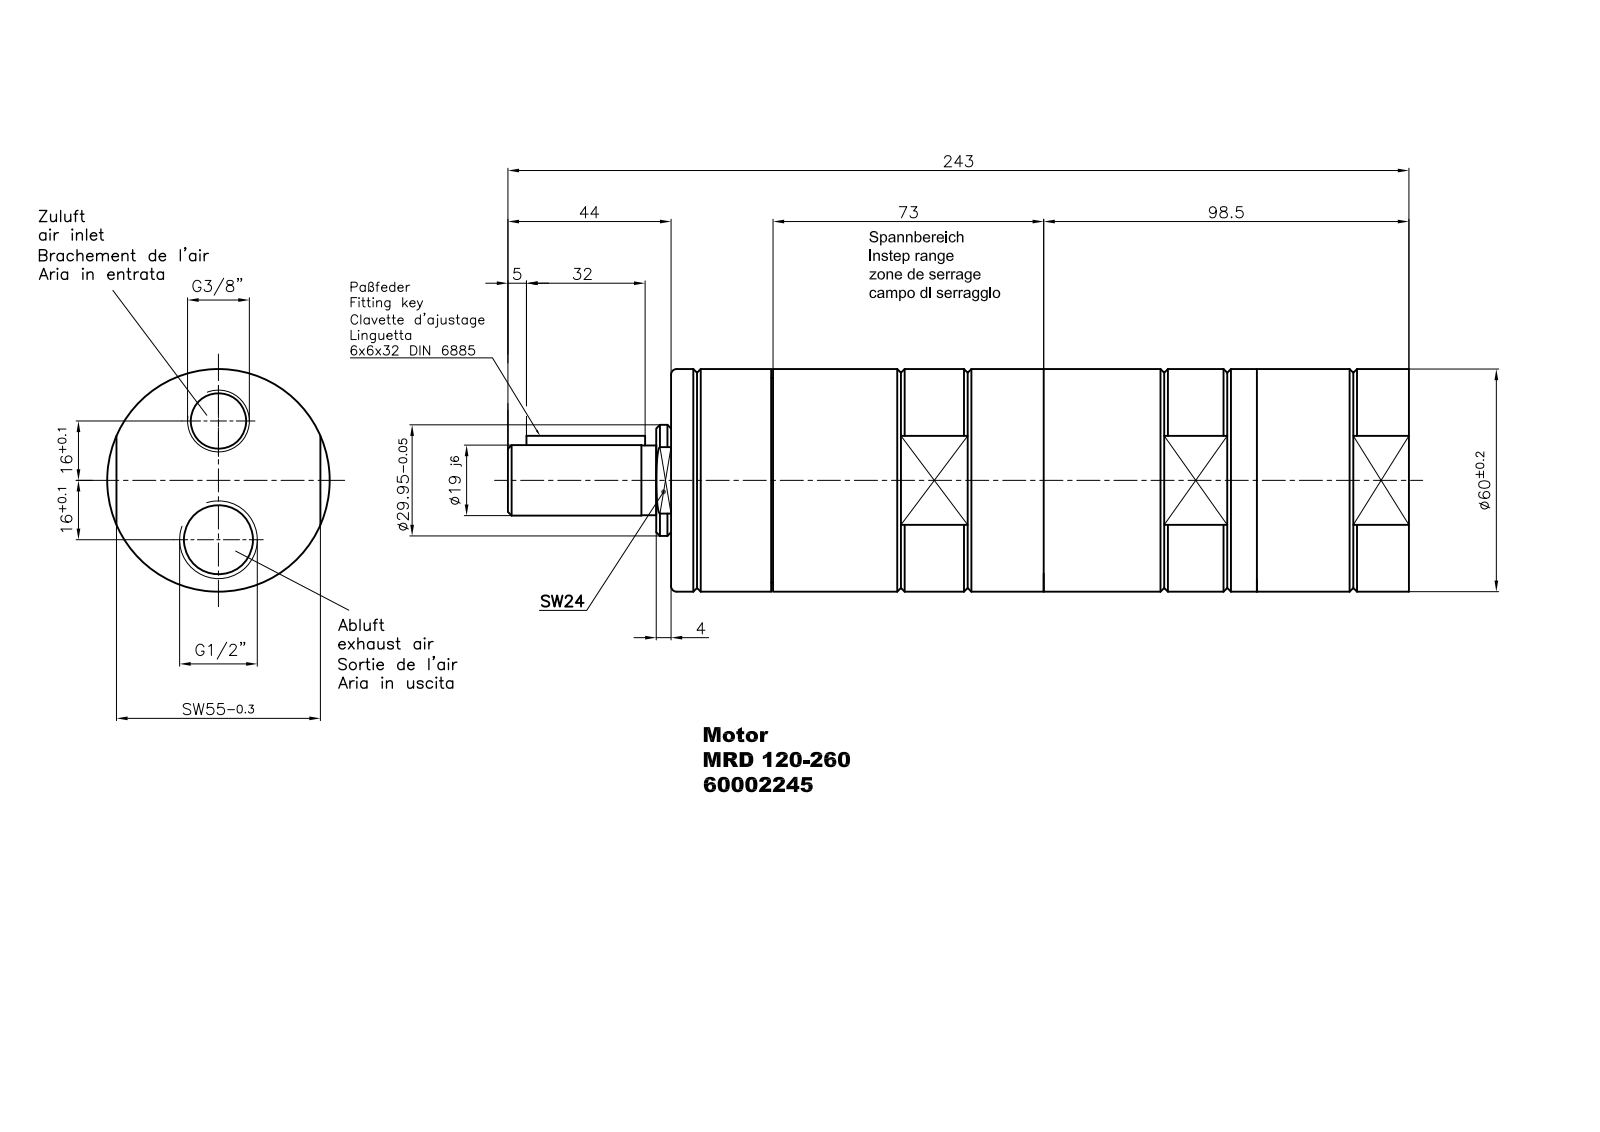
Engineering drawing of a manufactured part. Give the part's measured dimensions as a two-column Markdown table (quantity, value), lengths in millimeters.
| quantity | value |
| --- | --- |
| part name | MRD 120-260_60002245 |
| STEP written by | Autodesk Inventor 2008 (CONFIG_CONTROL_DESIGN) |
| units | millimeters |
| bodies | 1 solid, 122 faces (45 planar, 36 cylindrical, 41 other) |
| overall size | 243 × 60 × 60 |
| volume | 558 661 mm³ |
| surface area | 51 566 mm² |
| round holes (diameter × count) | 1.55 × 1, 4 × 1, 5.5 × 1, 35 × 1 |
| round bosses / shafts (diameter × count) | 60 × 1, 57.73 × 1, 29.95 × 1, 19 × 1, 18.8 × 1, 5 × 1, 3.6 × 1 |
| partial cylindrical surfaces (radius × count) | 3 × 2, 7.5 × 2, 8.5 × 1, 23.5 × 1, 26.68 × 1 |
| main face-to-face distances | 199, 55, 180.7, 18.3, 186, 5.3, 13, 4, 184.7, 190 |
